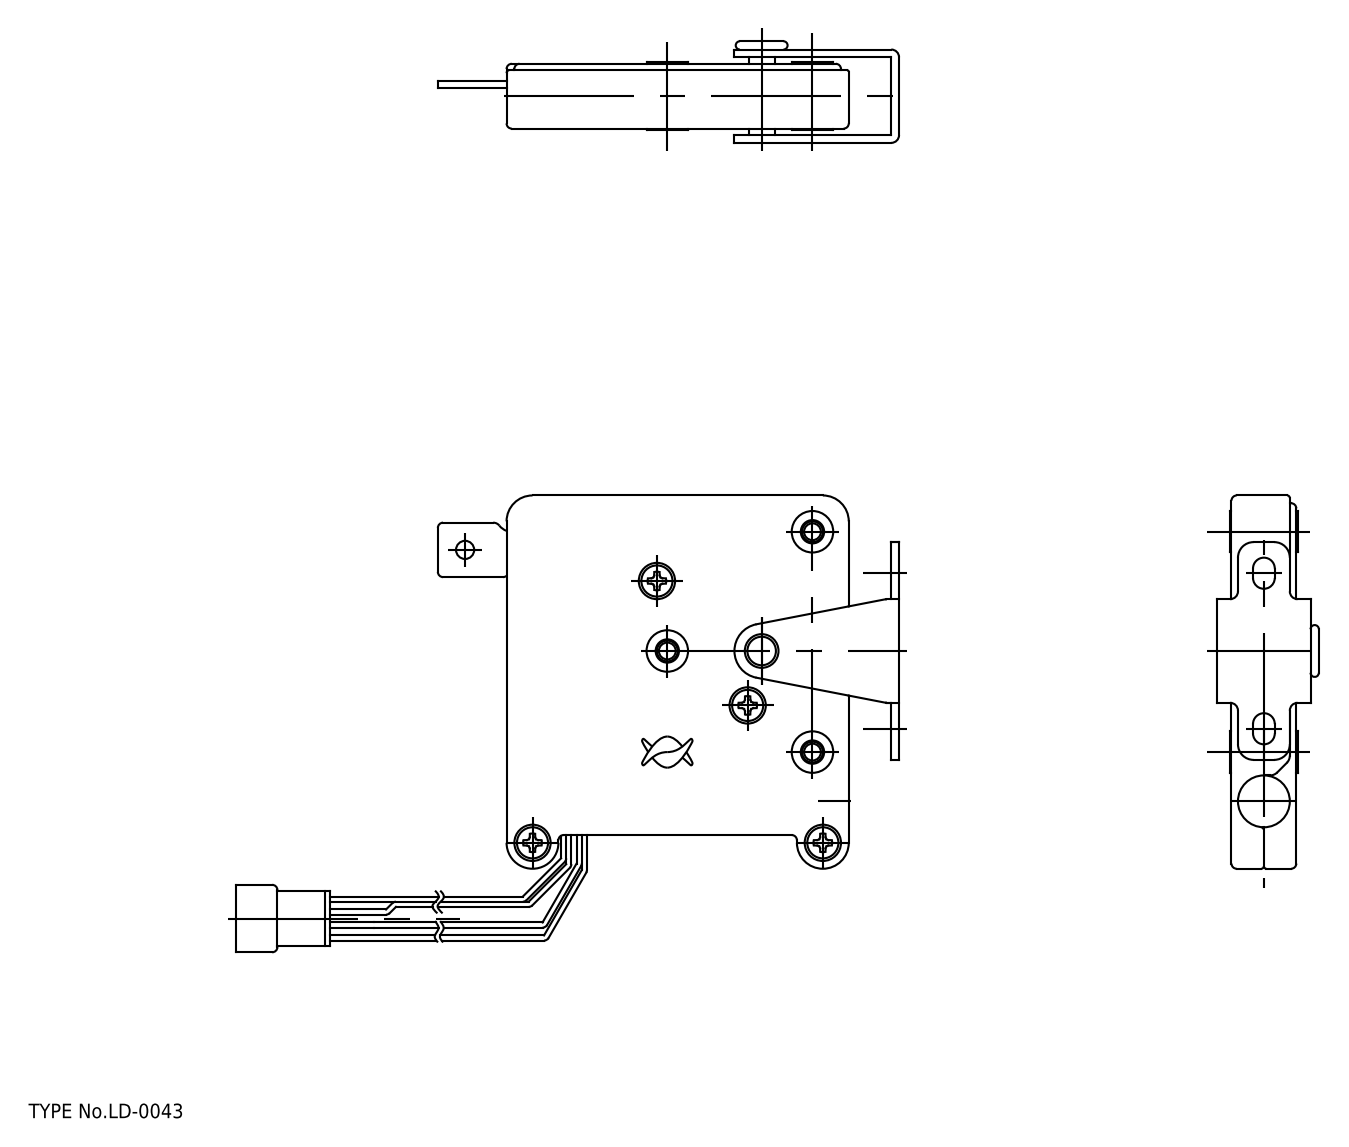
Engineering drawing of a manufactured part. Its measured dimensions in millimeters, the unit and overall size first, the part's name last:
Units: millimetres
Overall size (bounding box): 127.75 × 85.5 × 19.6
Round holes (diameter × count): ⌀4 ×4, ⌀4.5 ×3, ⌀2.5 ×1, ⌀3.5 ×1, ⌀5.2 ×1, ⌀10 ×1
Round bosses / shafts (diameter × count): ⌀1 ×16, ⌀6 ×4, ⌀8 ×3, ⌀6.5 ×3, ⌀6.2 ×2, ⌀2 ×2, ⌀10 ×1, ⌀5 ×1
Partial cylindrical surfaces — rounded edges, fillets, slot ends (radius × count): R0.5 ×183, R0.3 ×67, R1 ×46, R0.6 ×16, R3 ×11, R2 ×10, R5 ×8, R1.5 ×7
Main face-to-face distances: 1.25, 11.25, 12.5, 10, 1.5, 3, 2.75, 16.5, 13.75, 15.25
Hole centre spacings: 34.12, 11, 13.65, 26.68, 31.47, 34.95, 36.24, 37.01
Volume: 23 789 mm³ · Surface area: 29 927 mm²
Bodies: 2 solids, 2167 faces (1199 planar, 602 cylindrical, 366 other)
Part name (STEP PRODUCT): LD-0043(本体); LD-0043(キーパー)
STEP written by: spGate 17.5.1 (AUTOMOTIVE_DESIGN)
